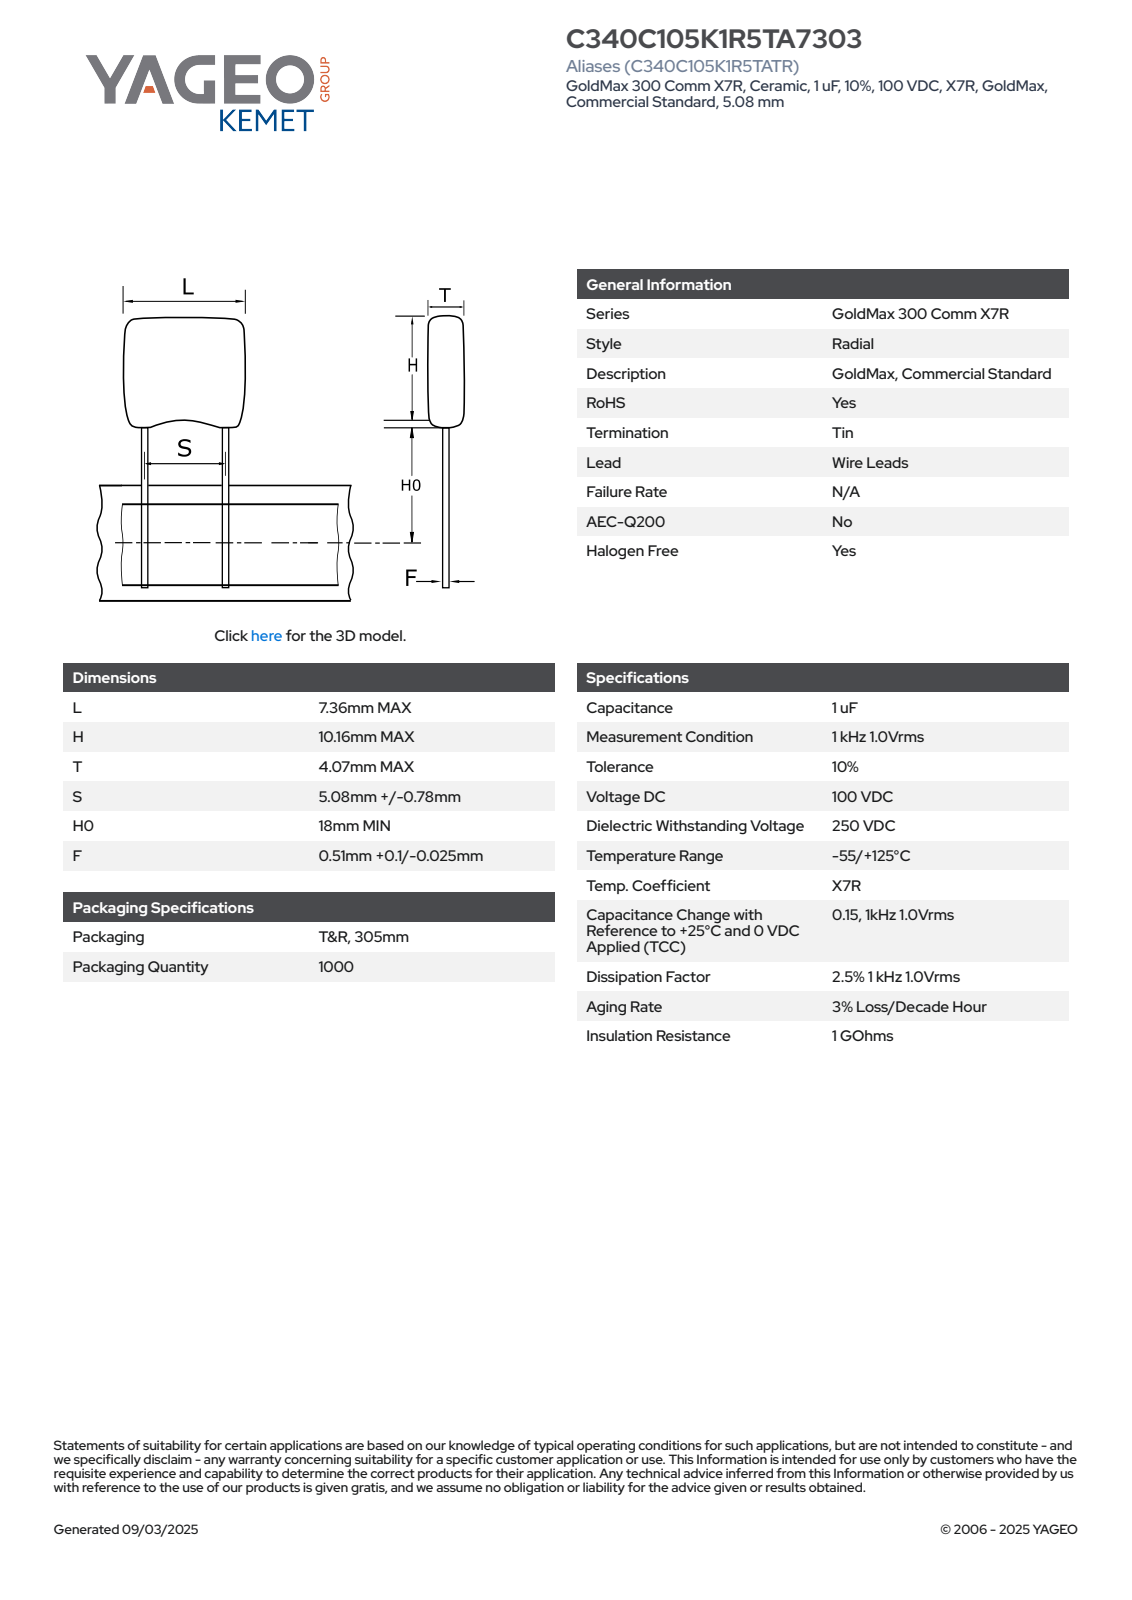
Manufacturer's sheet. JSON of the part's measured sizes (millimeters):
{"part_name": "CCR_KRCST_C340_L7.36H10.16T4.07S5.08H018F0.61", "step_written_by": "SolidWorks 2014 (AUTOMOTIVE_DESIGN)", "units": "millimeters", "bodies": {"solids": 4, "faces": 94, "planar": 66, "cylindrical": 18, "other": 10}, "overall_size": [29.32, 7.36, 4.08], "volume_mm3": 325, "surface_area_mm2": 359, "round_bosses_or_shafts": [[0.61, 2]], "partial_cylinders_radius": [[0.75, 12]], "face_to_face_distances": [4.07, 7.36, 11.32, 4.08, 18, 29.32, 23.77, 5.77, 5.55, 23.03]}
